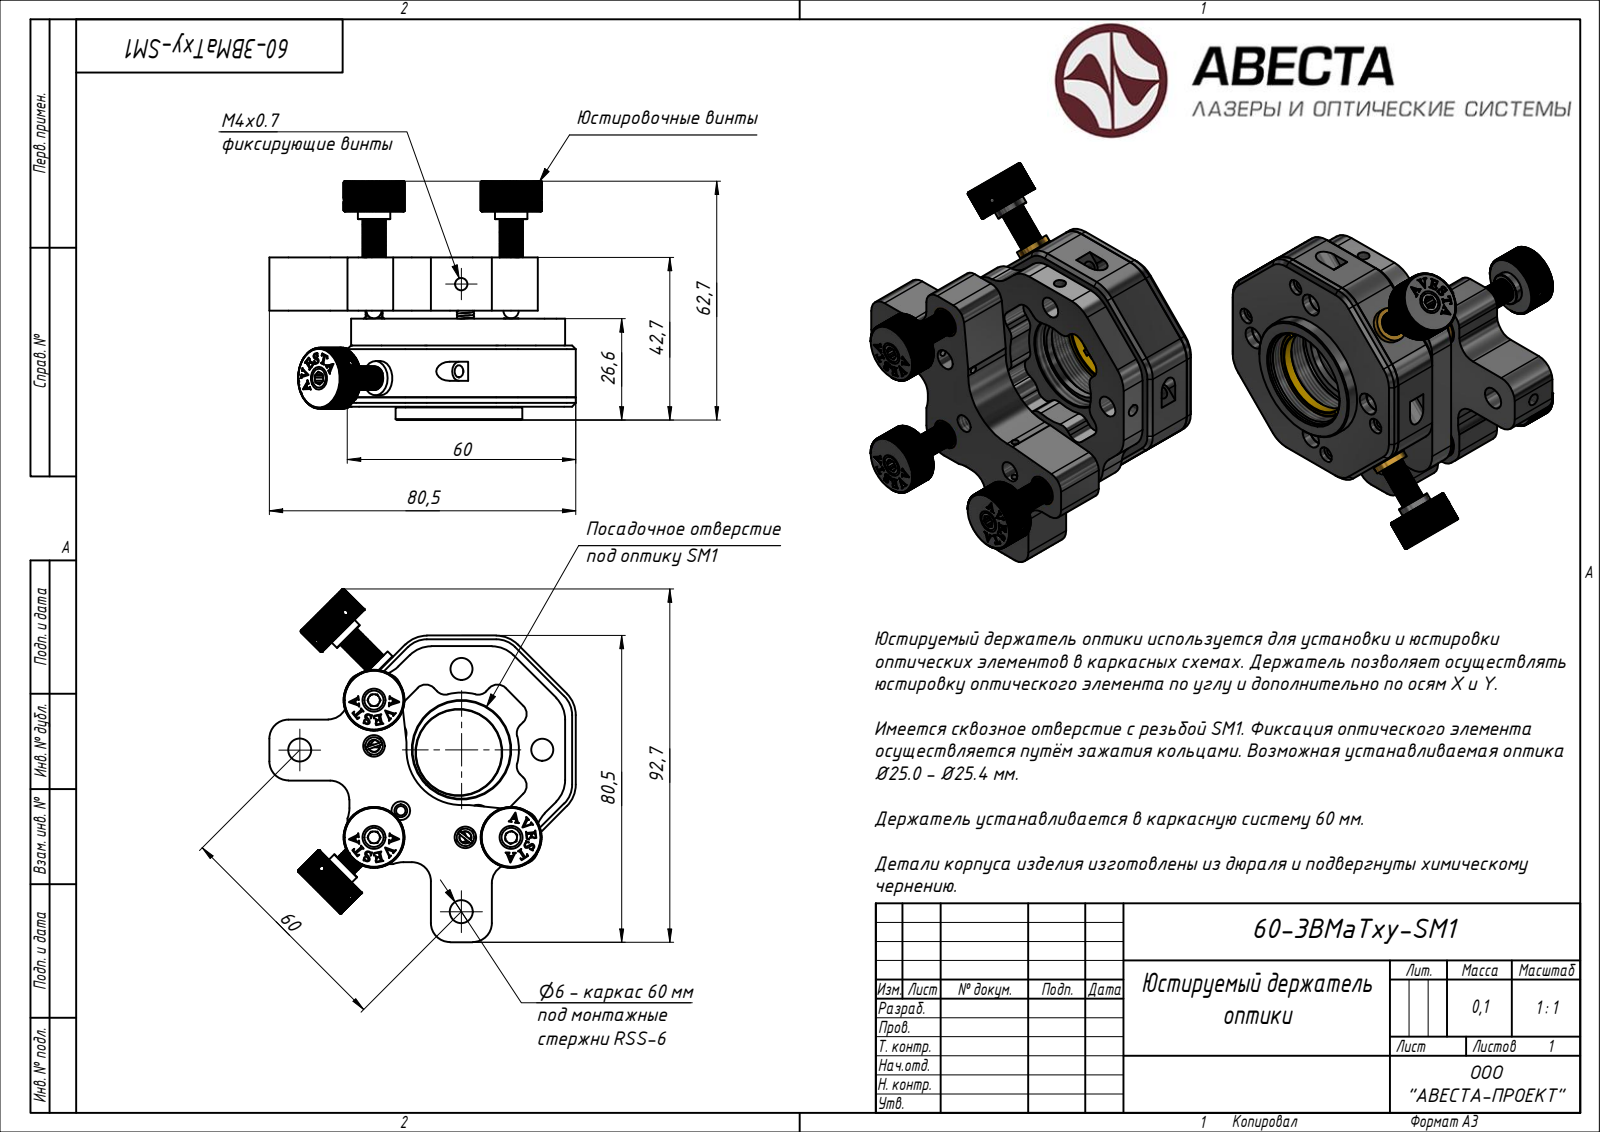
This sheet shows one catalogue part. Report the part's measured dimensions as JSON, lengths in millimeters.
{"step_written_by": "Rhino 7.34 (AUTOMOTIVE_DESIGN)", "units": "millimeters", "bodies": {"solids": 14, "faces": 4672, "planar": 2638, "cylindrical": 1392, "other": 642}, "overall_size": [93.41, 80.49, 61.7], "volume_mm3": 85355, "surface_area_mm2": 34789, "round_holes": [[1.57, 9], [3.24, 8], [3.1, 7], [2.2, 4], [4.3, 4], [6.02, 4], [6.1, 4], [8, 3], [10, 3], [1.57, 2], [2, 2], [5.6, 2]], "round_bosses_or_shafts": [[0.7, 6], [9, 5], [8.5, 5], [6, 5], [3.2, 2], [2.5, 2], [33.3, 1], [24.9, 1]], "partial_cylinders_radius": [[8, 22], [4, 21], [1.1, 12], [5, 10], [0.78, 7], [0.35, 5], [1.24, 5], [0.78, 4]], "face_to_face_distances": [39.7, 14, 23.1, 16.6, 25.7, 2.6, 7, 16.1, 9.6, 23.6], "hole_center_spacings": [13.1, 24.7, 19.09, 21.27, 28.64, 30, 45.61, 2.04]}
